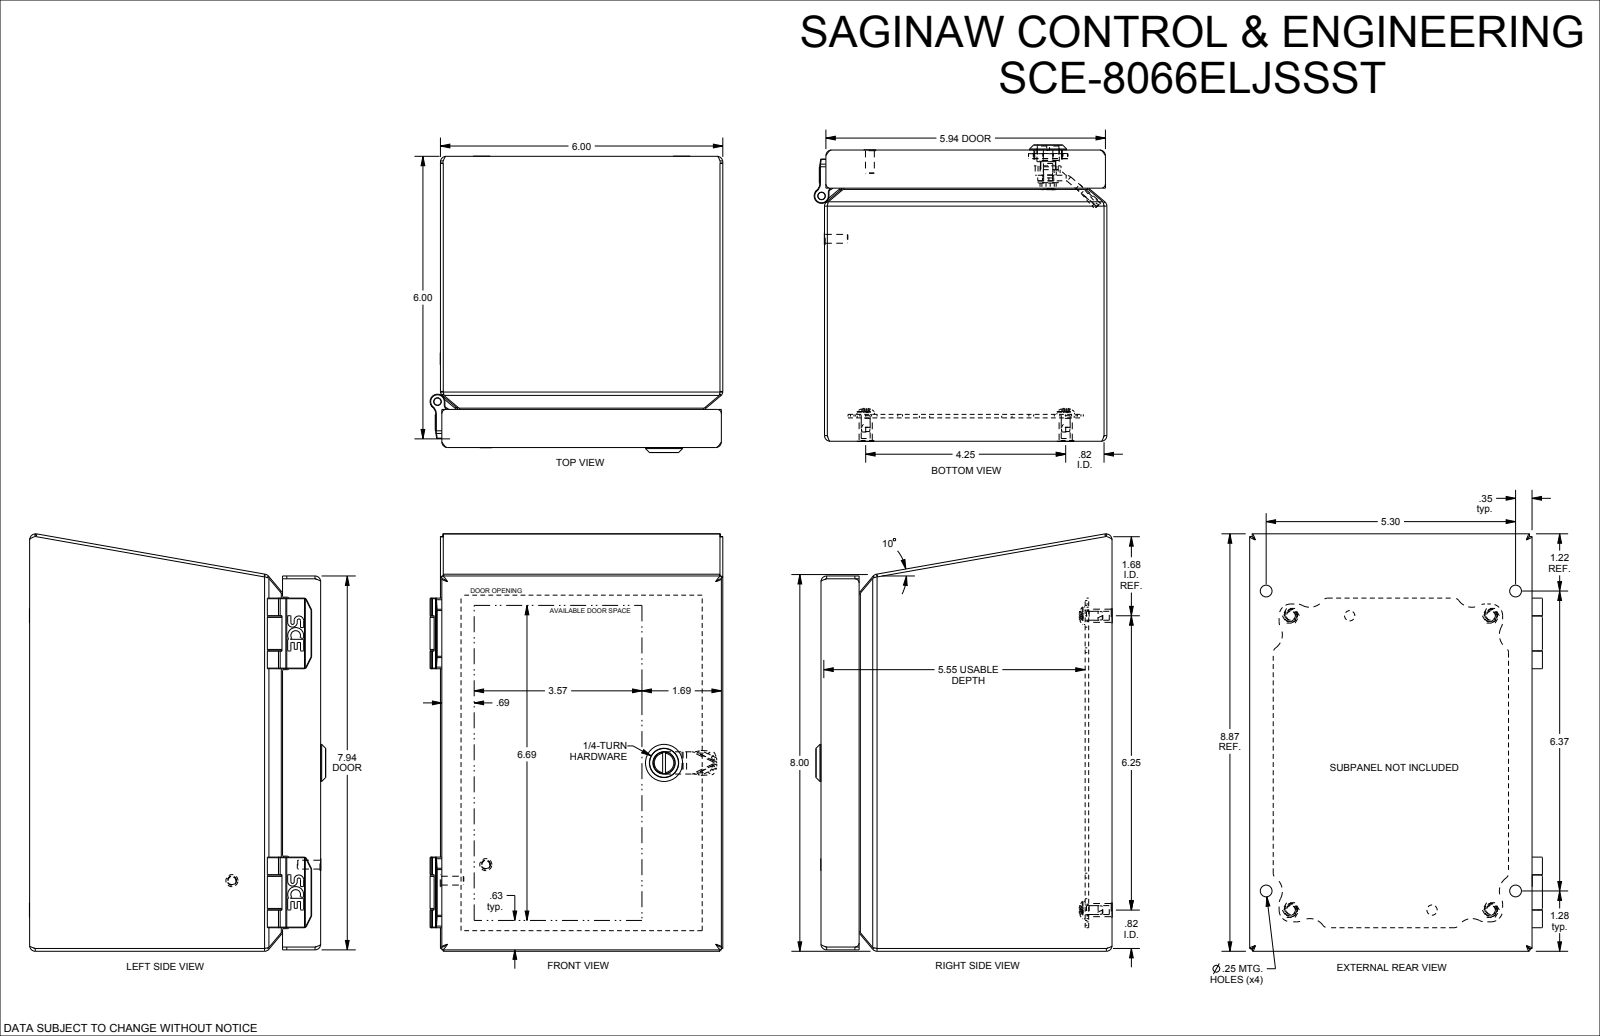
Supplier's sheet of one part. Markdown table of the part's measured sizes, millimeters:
| quantity | value |
| --- | --- |
| part name | SCE-8066ELJSSST |
| STEP written by | SolidWorks 2021 (AUTOMOTIVE_DESIGN) |
| units | millimeters |
| bodies | 34 solids, 1454 faces (566 planar, 353 cylindrical, 535 other) |
| overall size | 225.1 × 159.9 × 158 |
| volume | 368 500 mm³ |
| surface area | 457 800 mm² |
| round holes (diameter × count) | 4.1 × 4, 4.8 × 4, 6.4 × 4, 7.2 × 4, 0.5 × 2, 2.5 × 2, 5.5 × 2, 6.8 × 2, 4 × 1, 5 × 1, 5.1 × 1, 6.1 × 1 |
| round bosses / shafts (diameter × count) | 4.8 × 6, 12.3 × 4, 9.5 × 4, 7.1 × 4, 6 × 4, 4.1 × 4, 6.6 × 2, 6.5 × 2 |
| partial cylindrical surfaces (radius × count) | 0.8 × 50, 0.2 × 24, 0.3 × 21, 6.4 × 13, 3.2 × 11, 0.3 × 10, 1.5 × 10, 8.7 × 8 |
| main face-to-face distances | 1.5, 150.9, 1.5, 157.1, 155.6, 155.6, 154.1, 152.4, 149.4, 14.5 |
| hole center spacings | 139.7, 0.5, 16.8, 26.1, 31.8, 76.2, 79.9, 108 |
